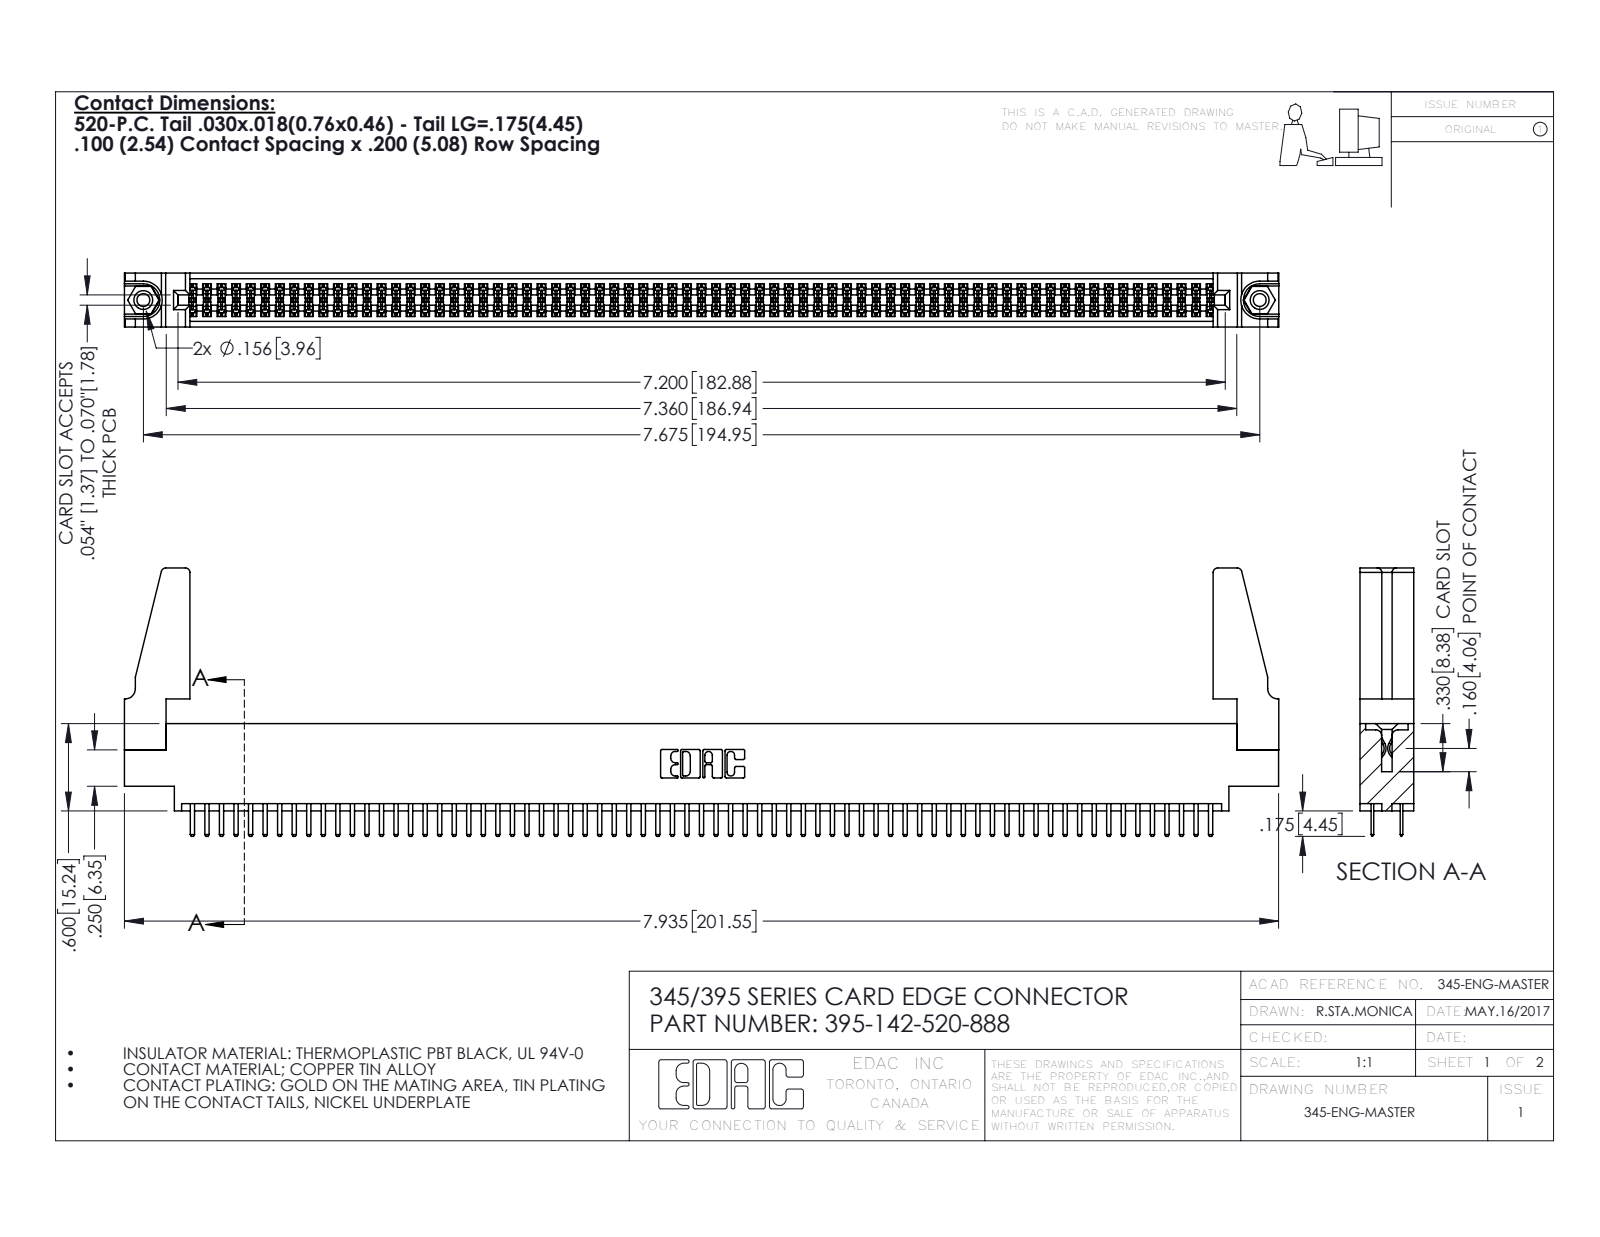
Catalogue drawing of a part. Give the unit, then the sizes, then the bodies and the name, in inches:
Units: inches
Overall size (bounding box): 7.936 × 1.845 × 0.37
Round holes (diameter × count): ⌀0.089 ×2, ⌀0.125 ×2, ⌀0.156 ×2, ⌀0.064 ×1
Round bosses / shafts (diameter × count): ⌀0.155 ×2
Partial cylindrical surfaces — rounded edges, fillets, slot ends (radius × count): R0.006 ×213, R0.01 ×146, R0.01 ×22, R0.03 ×8, R0.007 ×6, R0.031 ×6, R0.026 ×3, R0.014 ×2
Main face-to-face distances: 0.072, 0.298, 0.37, 0.2, 0.098, 0.272, 0.025, 0.225, 0.022, 0.072
Hole centre spacings: 0.27, 7.439, 7.675
Volume: 1.399 in³ · Surface area: 50.8 in²
Bodies: 147 solids, 7922 faces (5126 planar, 2780 cylindrical, 16 other)
Part name (STEP PRODUCT): 345-292-001_345-293-120; 395-142-520-888; 345-250-001_345-250-001-102; 345 Part_0.170 Offset - 0.156 Dia-TH (+1 more)
STEP written by: SolidWorks 2016 (CONFIG_CONTROL_DESIGN)
